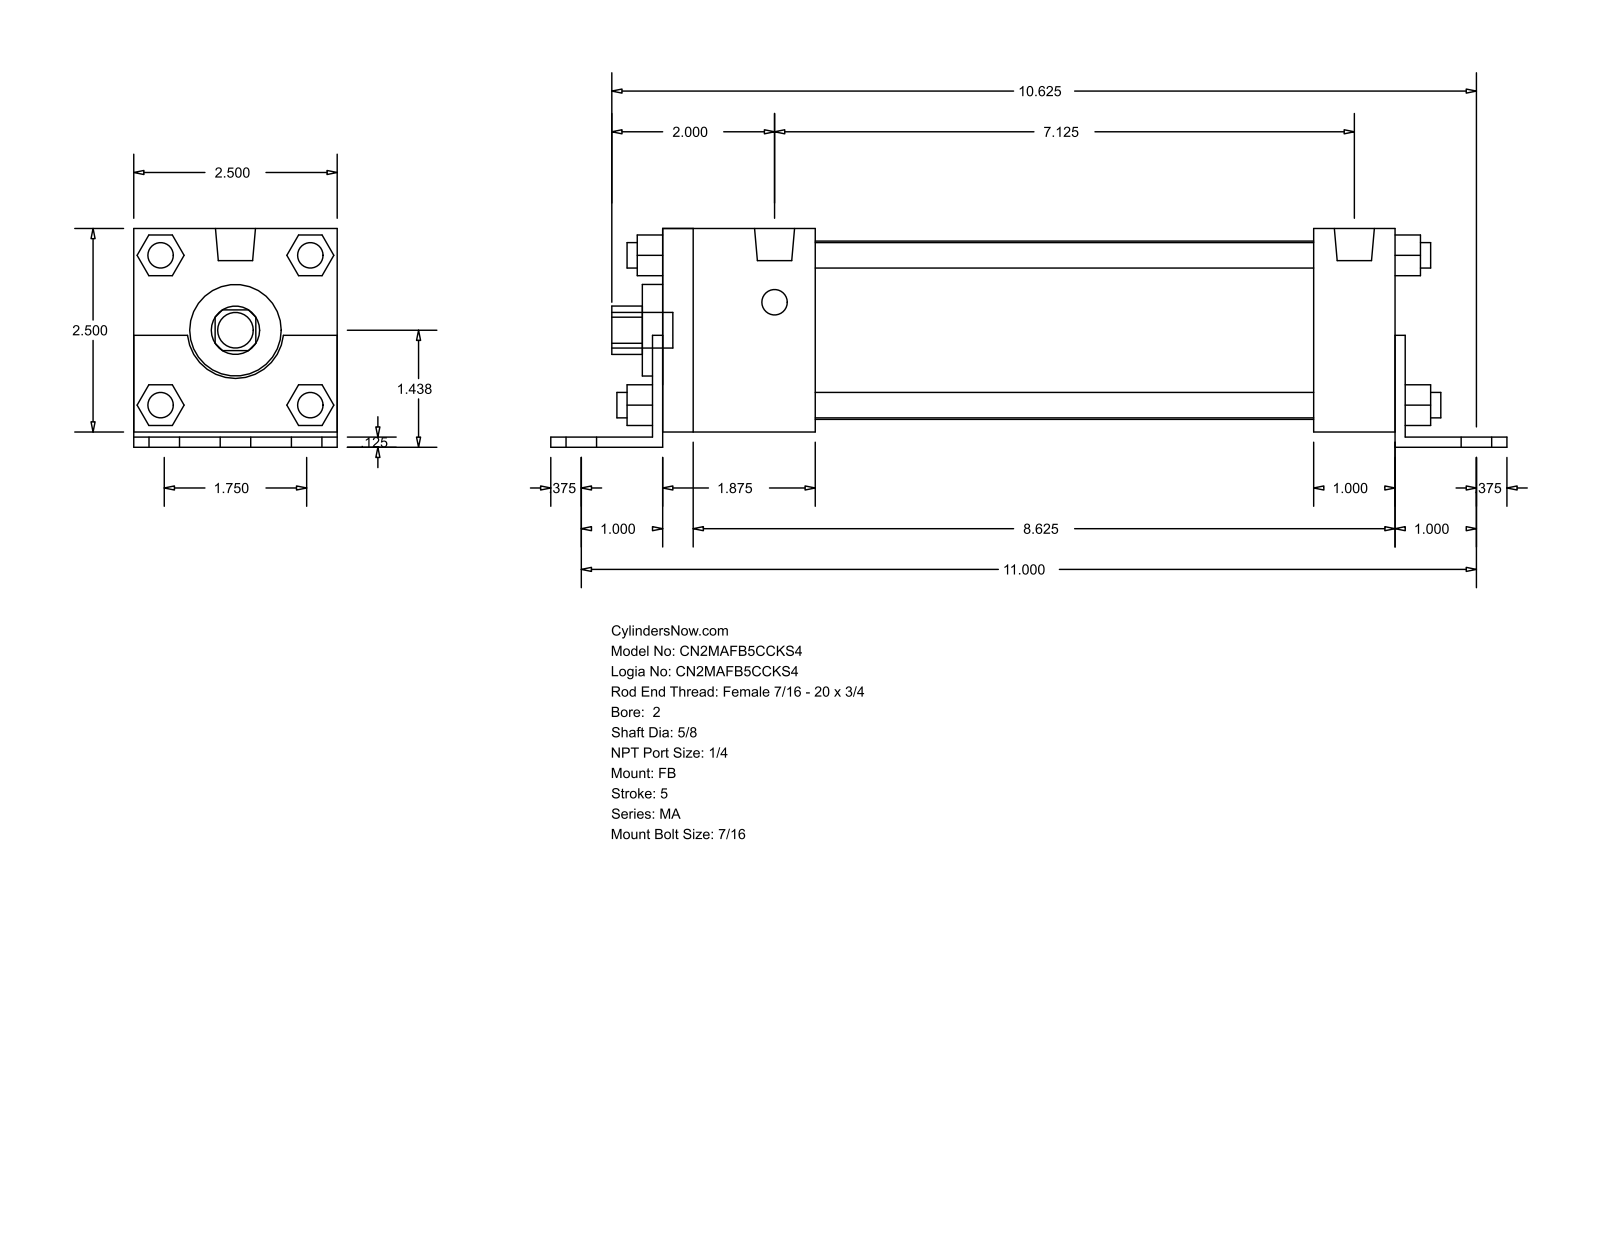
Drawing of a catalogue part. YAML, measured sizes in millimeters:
part_name: "MA_FB__0200_0.625"
step_written_by: "GSSL Pune (CONFIG_CONTROL_DESIGN)"
units: millimeters
bodies: {solids: 0, faces: 140, planar: 105, cylindrical: 35, other: 0}
overall_size: [298.45, 68.26, 63.5]
round_holes:
  - {diameter: 15.88, count: 1}
  - {diameter: 28.57, count: 1}
  - {diameter: 55.63, count: 1}
round_bosses_or_shafts:
  - {diameter: 7.94, count: 8}
  - {diameter: 11.11, count: 7}
  - {diameter: 12.49, count: 2}
partial_cylinders:
  - {radius: 7.54, count: 1}
  - {radius: 15.05, count: 1}
face_to_face_distances: [63.5, 4.76, 3.17, 68.26, 1.59, 3.18, 65.09, 231.77, 228.59, 25.4]
